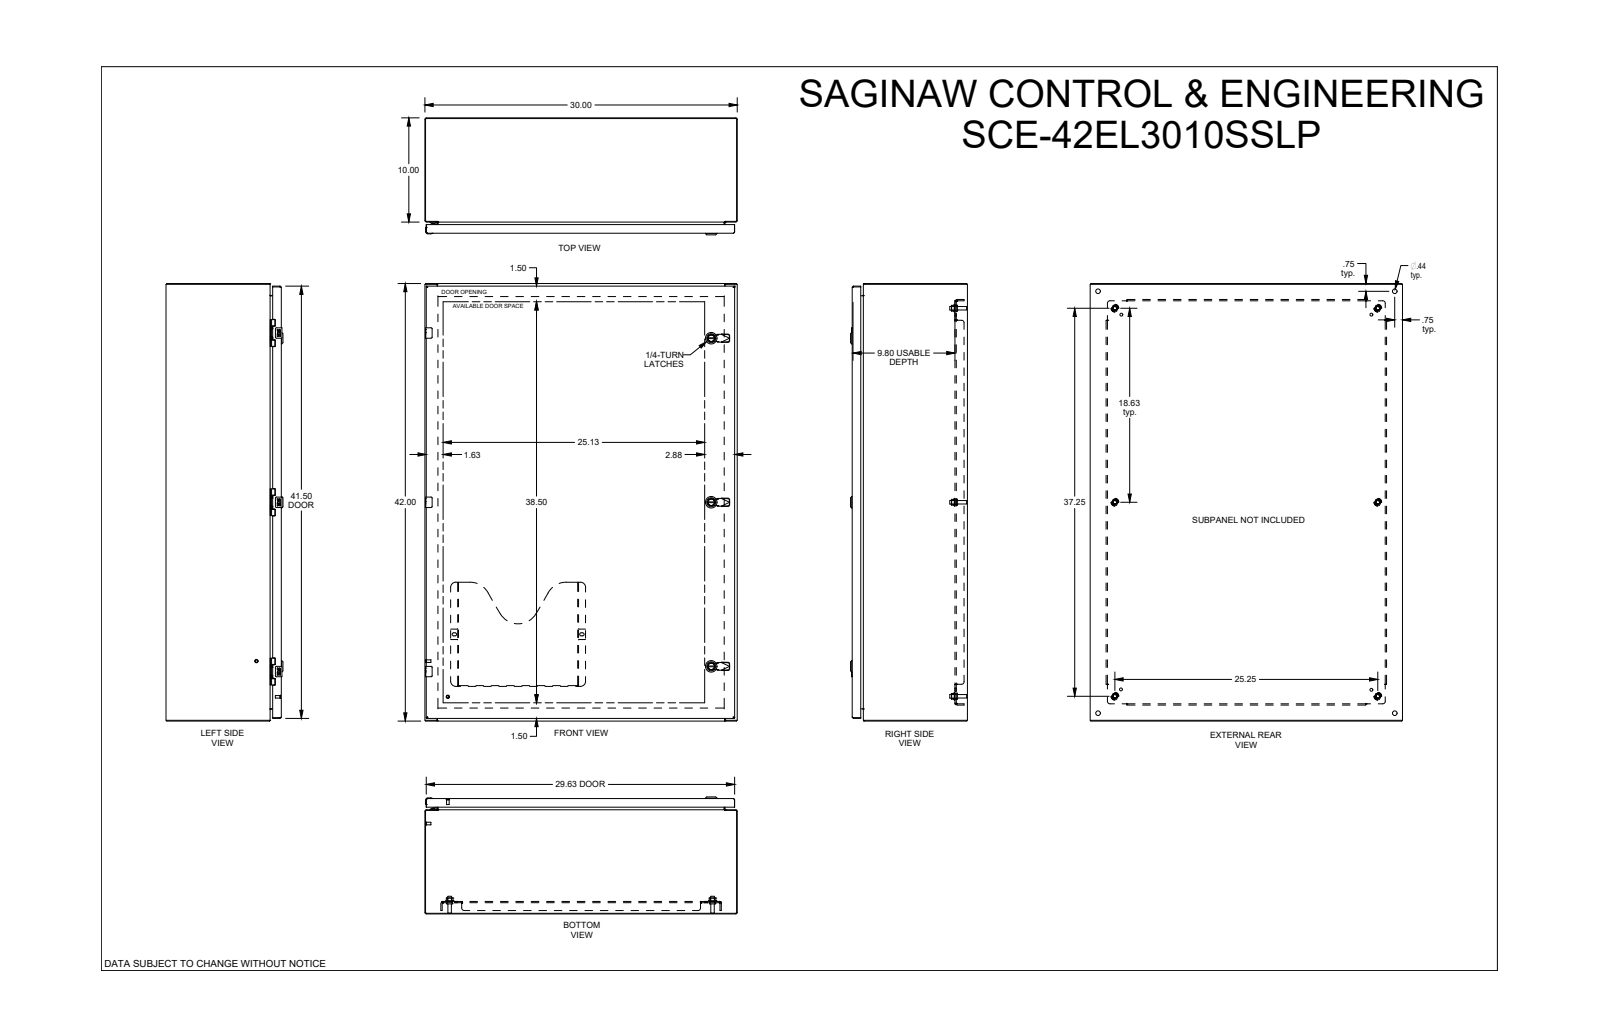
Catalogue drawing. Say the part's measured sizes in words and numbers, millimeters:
The part is named "SCE-42EL3010SSLP". Its 3-D file was written by "SolidWorks 2019 (CONFIG_CONTROL_DESIGN)". It is 0 solids with 3802 faces: 1798 planar, 1051 cylindrical and 953 other. Overall it measures 1066.8 by 762 by 285.2 millimeters. Round holes: 6 of diameter 4.4, 6 of diameter 5.2, 6 of diameter 6.2, 6 of diameter 6.8, 6 of diameter 9.3, 6 of diameter 12.7, 4 of diameter 7.1, 4 of diameter 9.5, 4 of diameter 11.1, 3 of diameter 4, 3 of diameter 5, 3 of diameter 5.5. Round bosses or shafts: 9 of diameter 4.3, 6 of diameter 9.3, 6 of diameter 8.4, 6 of diameter 6.4, 4 of diameter 6.3, 4 of diameter 5, 3 of diameter 28, 3 of diameter 22. Partial cylindrical surfaces (rounded edges, fillets, slot ends): 82 of radius 0.3, 40 of radius 0.3, 36 of radius 0.4, 28 of radius 0.5, 23 of radius 1, 14 of radius 1.8, 13 of radius 0.8, 12 of radius 0.7. The main face-to-face distances are 1.9, 1.9, 277.4, 279.3, 281.3, 279.3, 30.5, 250.8, 3.2, 25.4. The hole center spacings are 412.8, 25, 825.5, 0.5, 114.1, 387.7, 412.8, 412.8.
